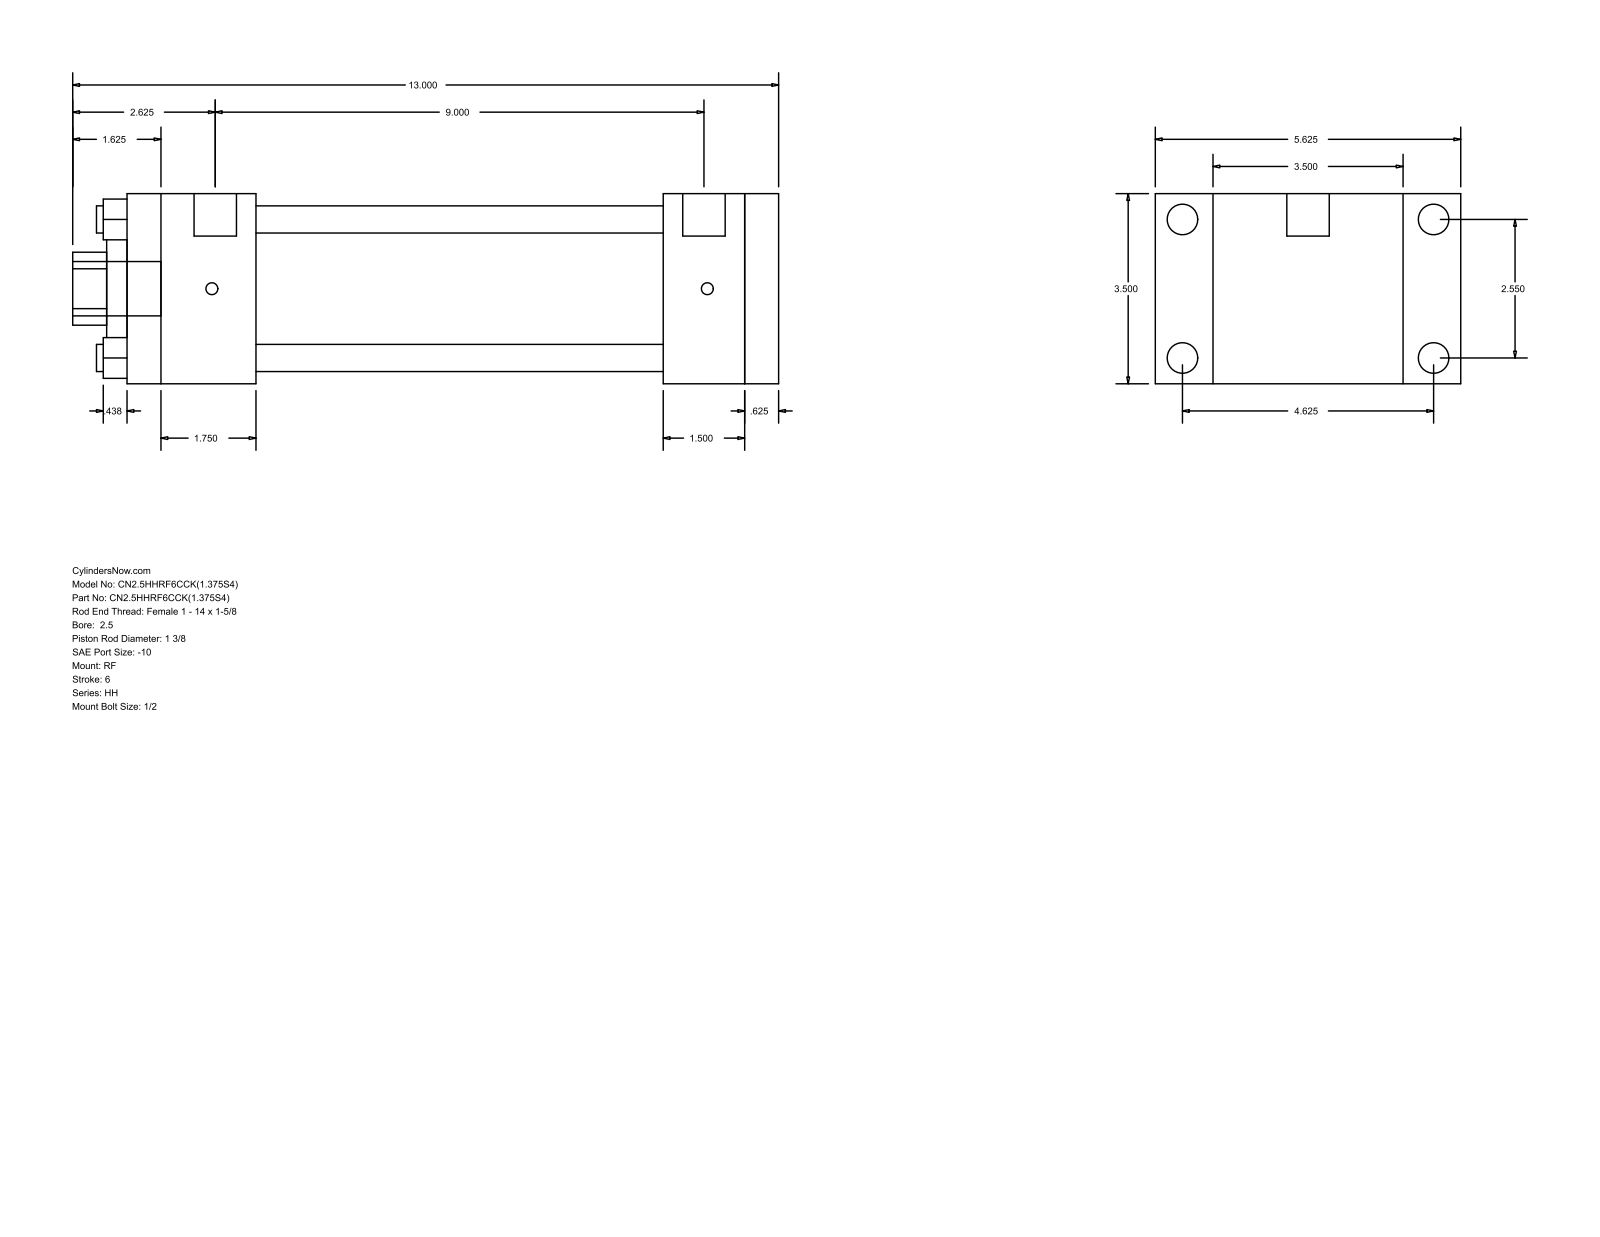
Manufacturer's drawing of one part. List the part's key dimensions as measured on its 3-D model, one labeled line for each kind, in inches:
Part name (STEP PRODUCT): HH_RF__0250_1.375
STEP written by: GSSL Pune (CONFIG_CONTROL_DESIGN)
Units: inches
Bodies: 0 solids, 92 faces (64 planar, 28 cylindrical, 0 other)
Overall size (bounding box): 13 × 5.625 × 3.5
Round holes (diameter × count): ⌀0.5 ×4, ⌀1.375 ×1, ⌀2 ×1, ⌀2.875 ×1
Round bosses / shafts (diameter × count): ⌀0.563 ×4, ⌀0.219 ×4, ⌀0.781 ×2, ⌀1 ×1
Partial cylindrical surfaces — rounded edges, fillets, slot ends (radius × count): R0.672 ×1
Main face-to-face distances: 3.5, 12, 0.625, 11.375, 2.375, 9, 9.625, 9.875, 7.5, 1.5
Hole centre spacings: 1.803, 2.55, 3.606
